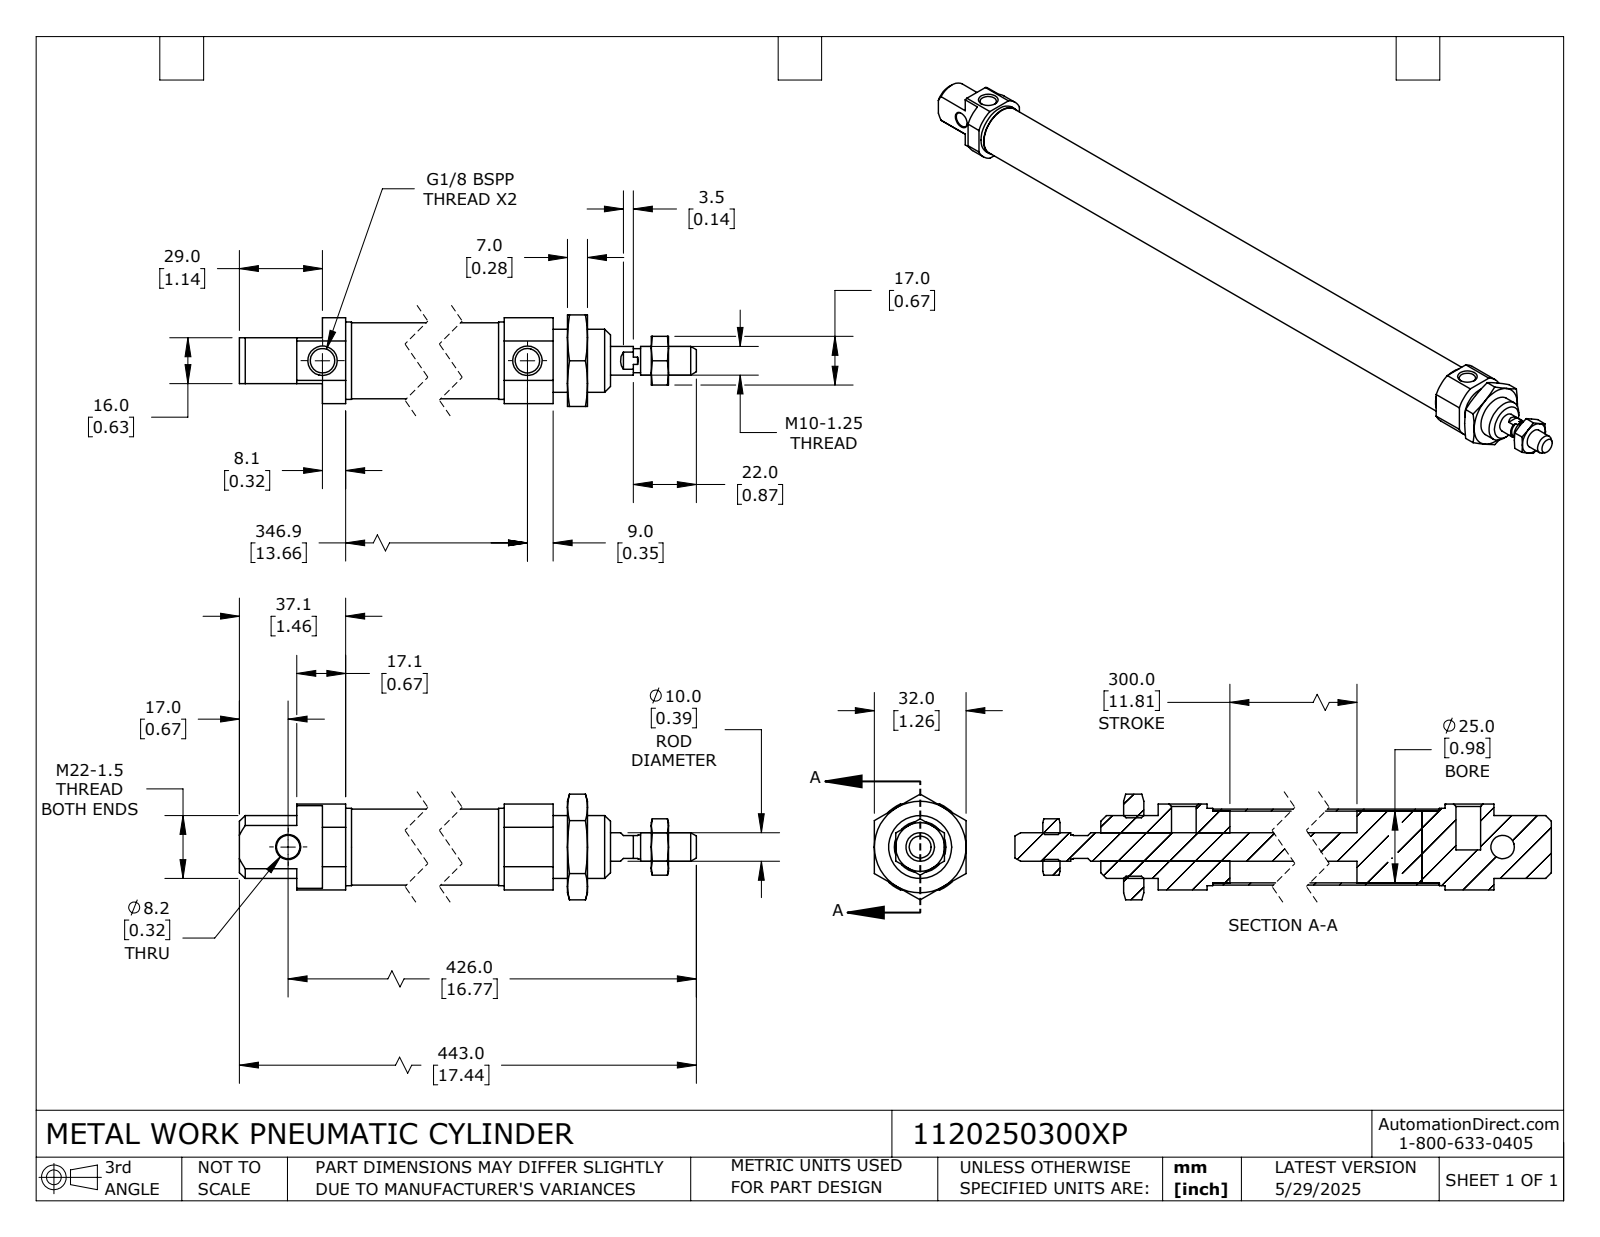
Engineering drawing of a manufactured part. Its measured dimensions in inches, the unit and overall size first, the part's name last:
Units: inches
Overall size (bounding box): 17.441 × 1.455 × 1.26
Round holes (diameter × count): ⌀0.337 ×2, ⌀0.323 ×1, ⌀0.341 ×1, ⌀0.802 ×1, ⌀0.984 ×1
Round bosses / shafts (diameter × count): ⌀1.063 ×1, ⌀1.044 ×1, ⌀0.99 ×1, ⌀0.866 ×1, ⌀0.394 ×1, ⌀0.331 ×1
Partial cylindrical surfaces — rounded edges, fillets, slot ends (radius × count): R0.65 ×1
Main face-to-face distances: 0.276, 0.315, 1.461, 0.906, 1.181, 14.484, 13.697, 0.988, 0.63, 13.024
Hole centre spacings: 13.976
Volume: 6.507 in³ · Surface area: 131 in²
Bodies: 6 solids, 144 faces (54 planar, 44 cylindrical, 46 other)
Part name (STEP PRODUCT): 1120250300XP_BODY; 1120250300XP_ROD; 1120250300XP
STEP written by: SolidWorks 2024 (CONFIG_CONTROL_DESIGN)
